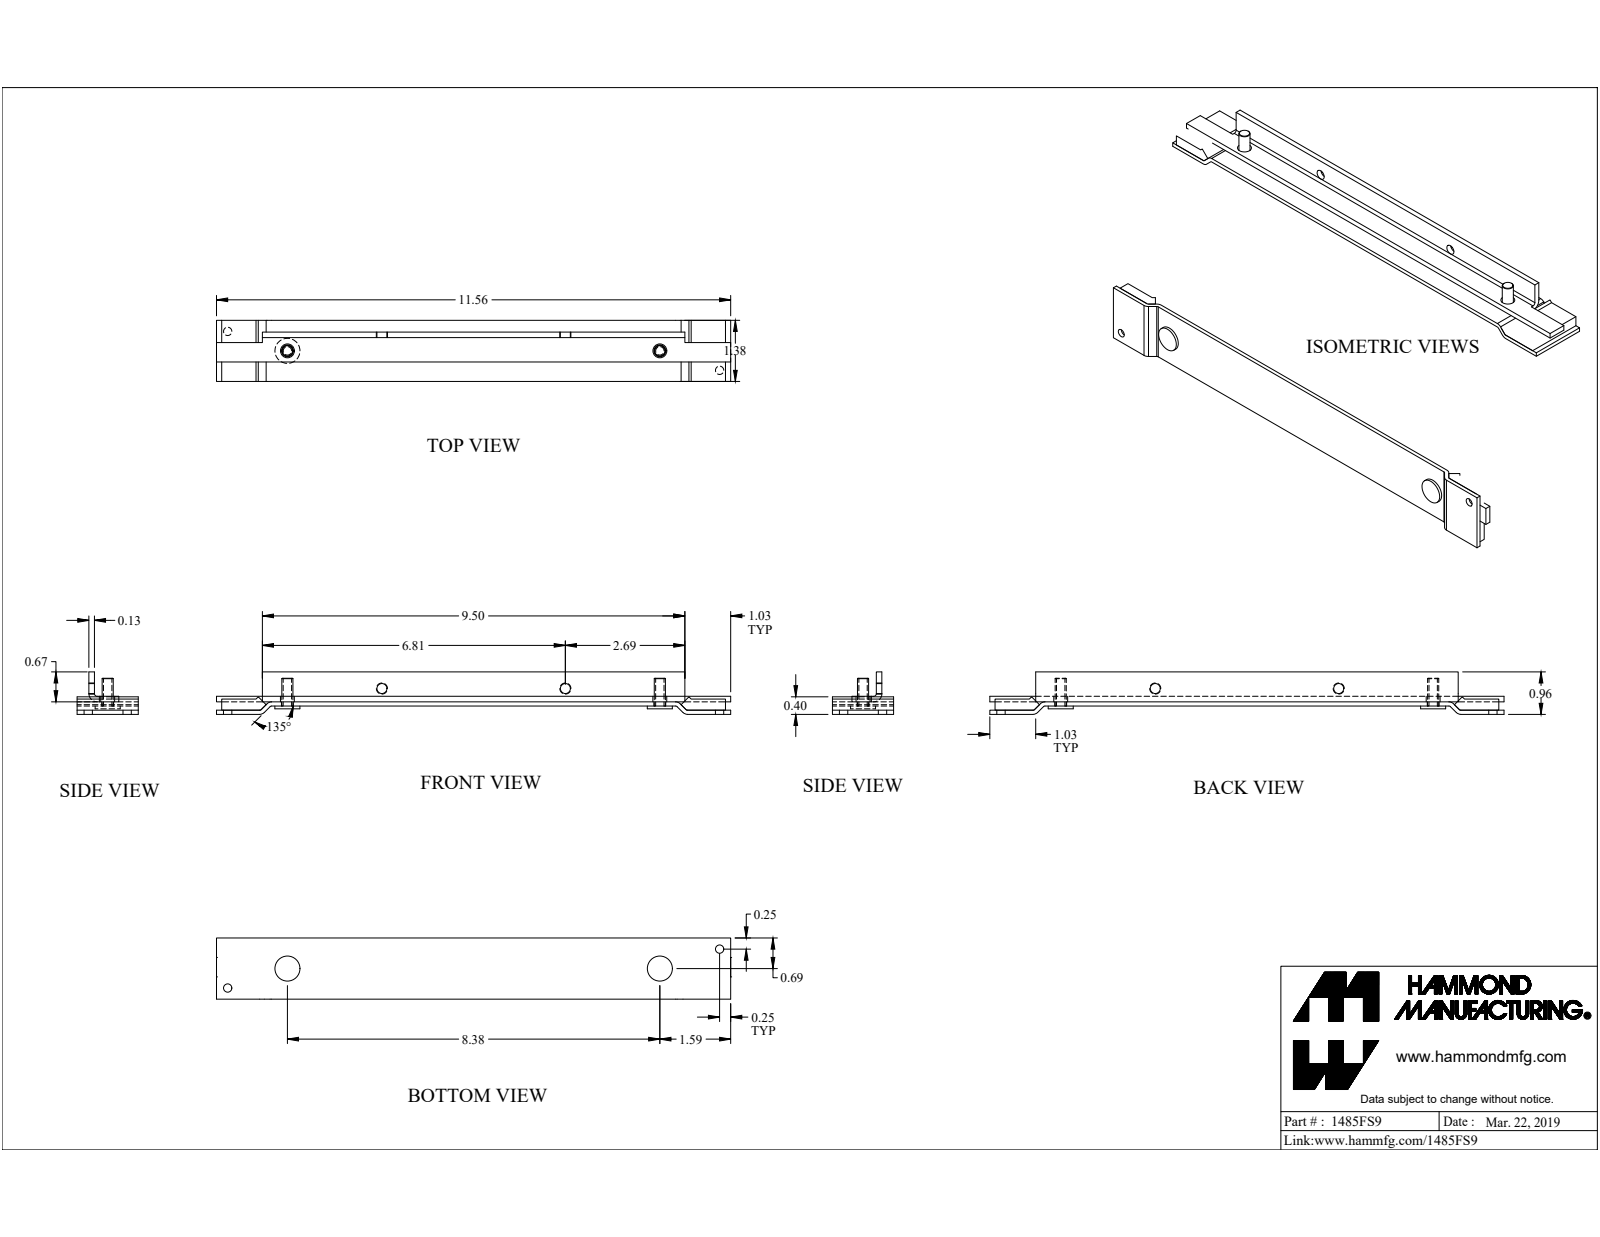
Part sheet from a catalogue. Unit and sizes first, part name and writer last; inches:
Units: inches
Overall size (bounding box): 11.563 × 1.375 × 0.956
Round holes (diameter × count): ⌀0.187 ×2, ⌀0.224 ×2, ⌀0.265 ×2, ⌀0.313 ×2
Round bosses / shafts (diameter × count): ⌀0.563 ×2, ⌀0.25 ×2
Partial cylindrical surfaces — rounded edges, fillets, slot ends (radius × count): R0.048 ×4, R0.143 ×4, R0.06 ×1, R0.185 ×1
Main face-to-face distances: 0.095, 0.125, 0.22, 0.093, 0.188, 0.313, 0.095, 0.283, 0.673, 0.548
Hole centre spacings: 1.413, 9.728, 4.125, 8.375, 11.097
Volume: 3.727 in³ · Surface area: 71.46 in²
Bodies: 6 solids, 72 faces (48 planar, 22 cylindrical, 2 other)
Part name (STEP PRODUCT): 1485FS9
STEP written by: SolidWorks 2019 (CONFIG_CONTROL_DESIGN)
